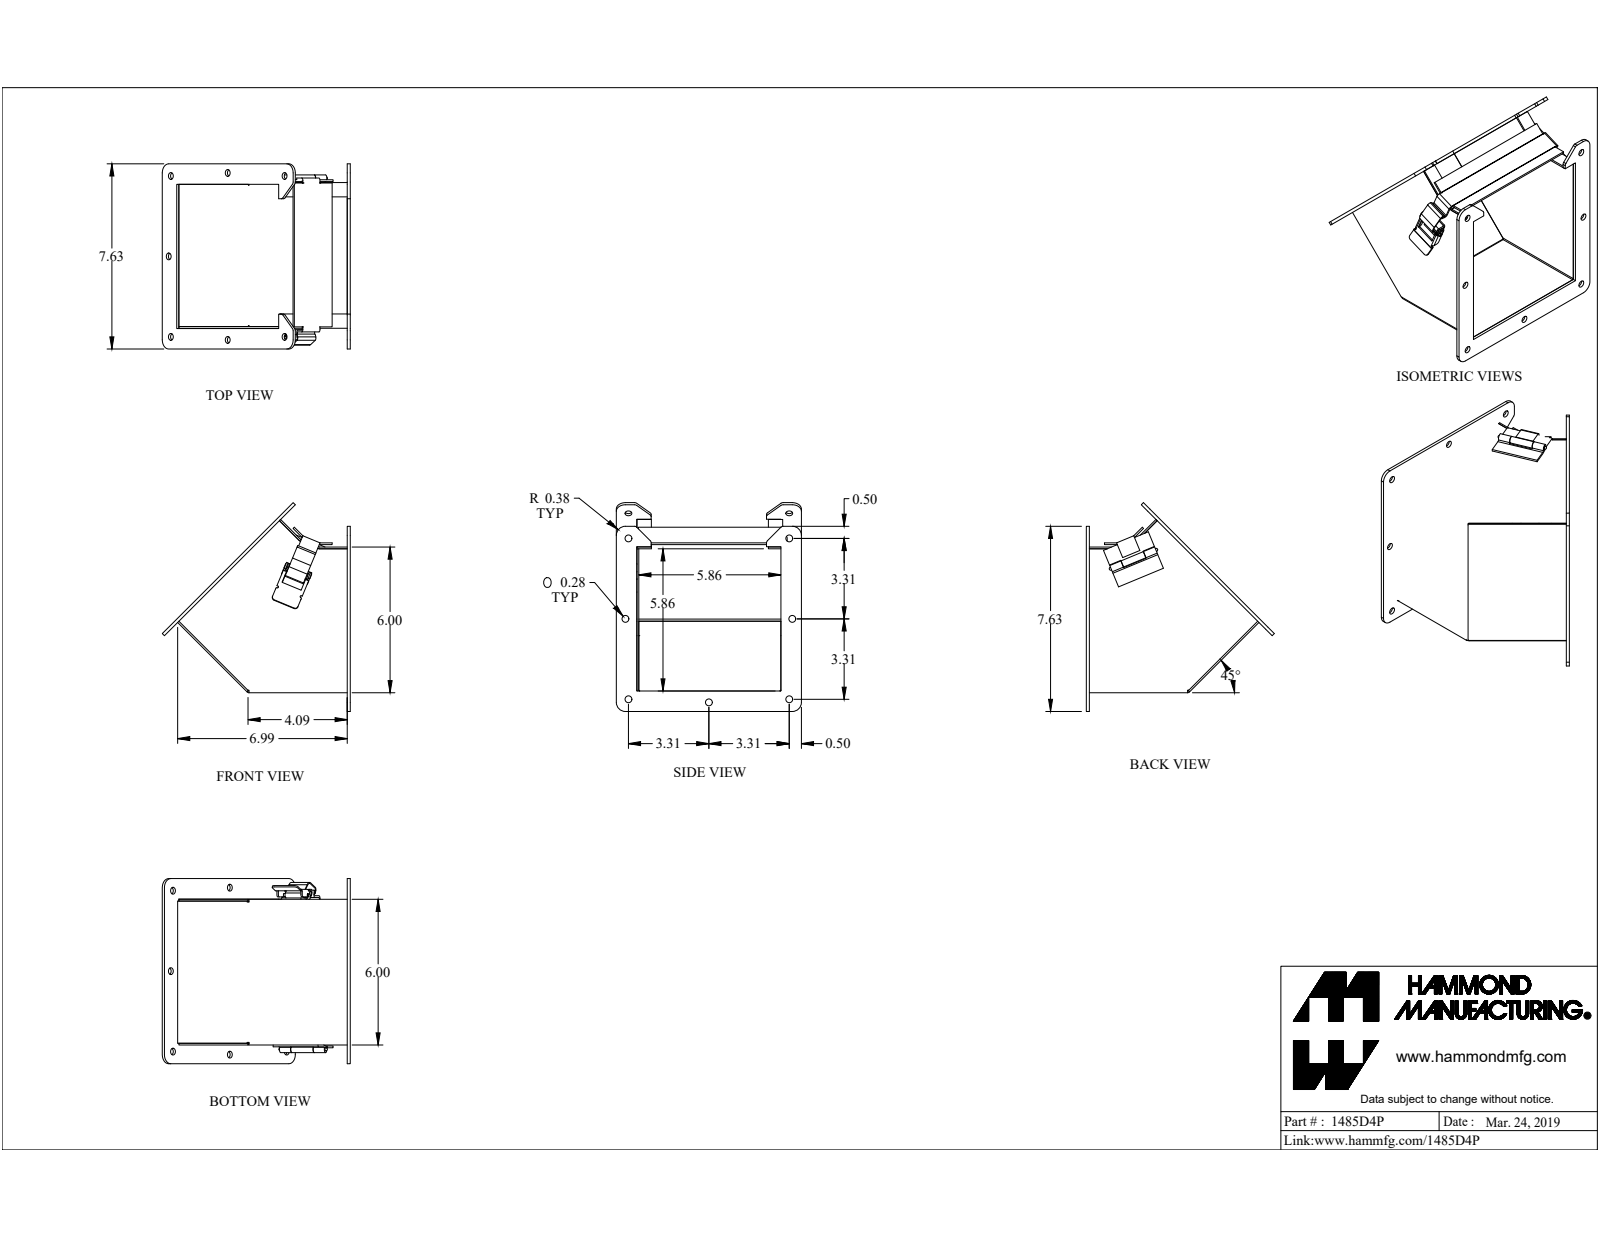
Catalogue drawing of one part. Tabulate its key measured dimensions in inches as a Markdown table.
| quantity | value |
| --- | --- |
| part name | 1485D4P |
| STEP written by | SolidWorks 2019 (CONFIG_CONTROL_DESIGN) |
| units | inches |
| bodies | 12 solids, 313 faces (198 planar, 113 cylindrical, 2 other) |
| overall size | 8.6 × 7.745 × 7.625 |
| volume | 14.45 in³ |
| surface area | 372.4 in² |
| round holes (diameter × count) | 0.281 × 14, 0.125 × 2, 0.13 × 2, 0.164 × 2 |
| round bosses / shafts (diameter × count) | 0.187 × 3, 0.275 × 2, 0.156 × 2, 0.125 × 1 |
| partial cylindrical surfaces (radius × count) | 0.125 × 12, 0.036 × 10, 0.108 × 10, 0.375 × 8, 0.016 × 7, 0.035 × 4, 0.039 × 4, 0.076 × 3 |
| main face-to-face distances | 0.072, 5.928, 0.125, 6, 5.856, 0.172, 6.1, 6.099, 0.843, 0.244 |
| hole center spacings | 7.519, 3.315, 6.625, 3.315, 6.404, 6.45, 9.369, 7.519 |
